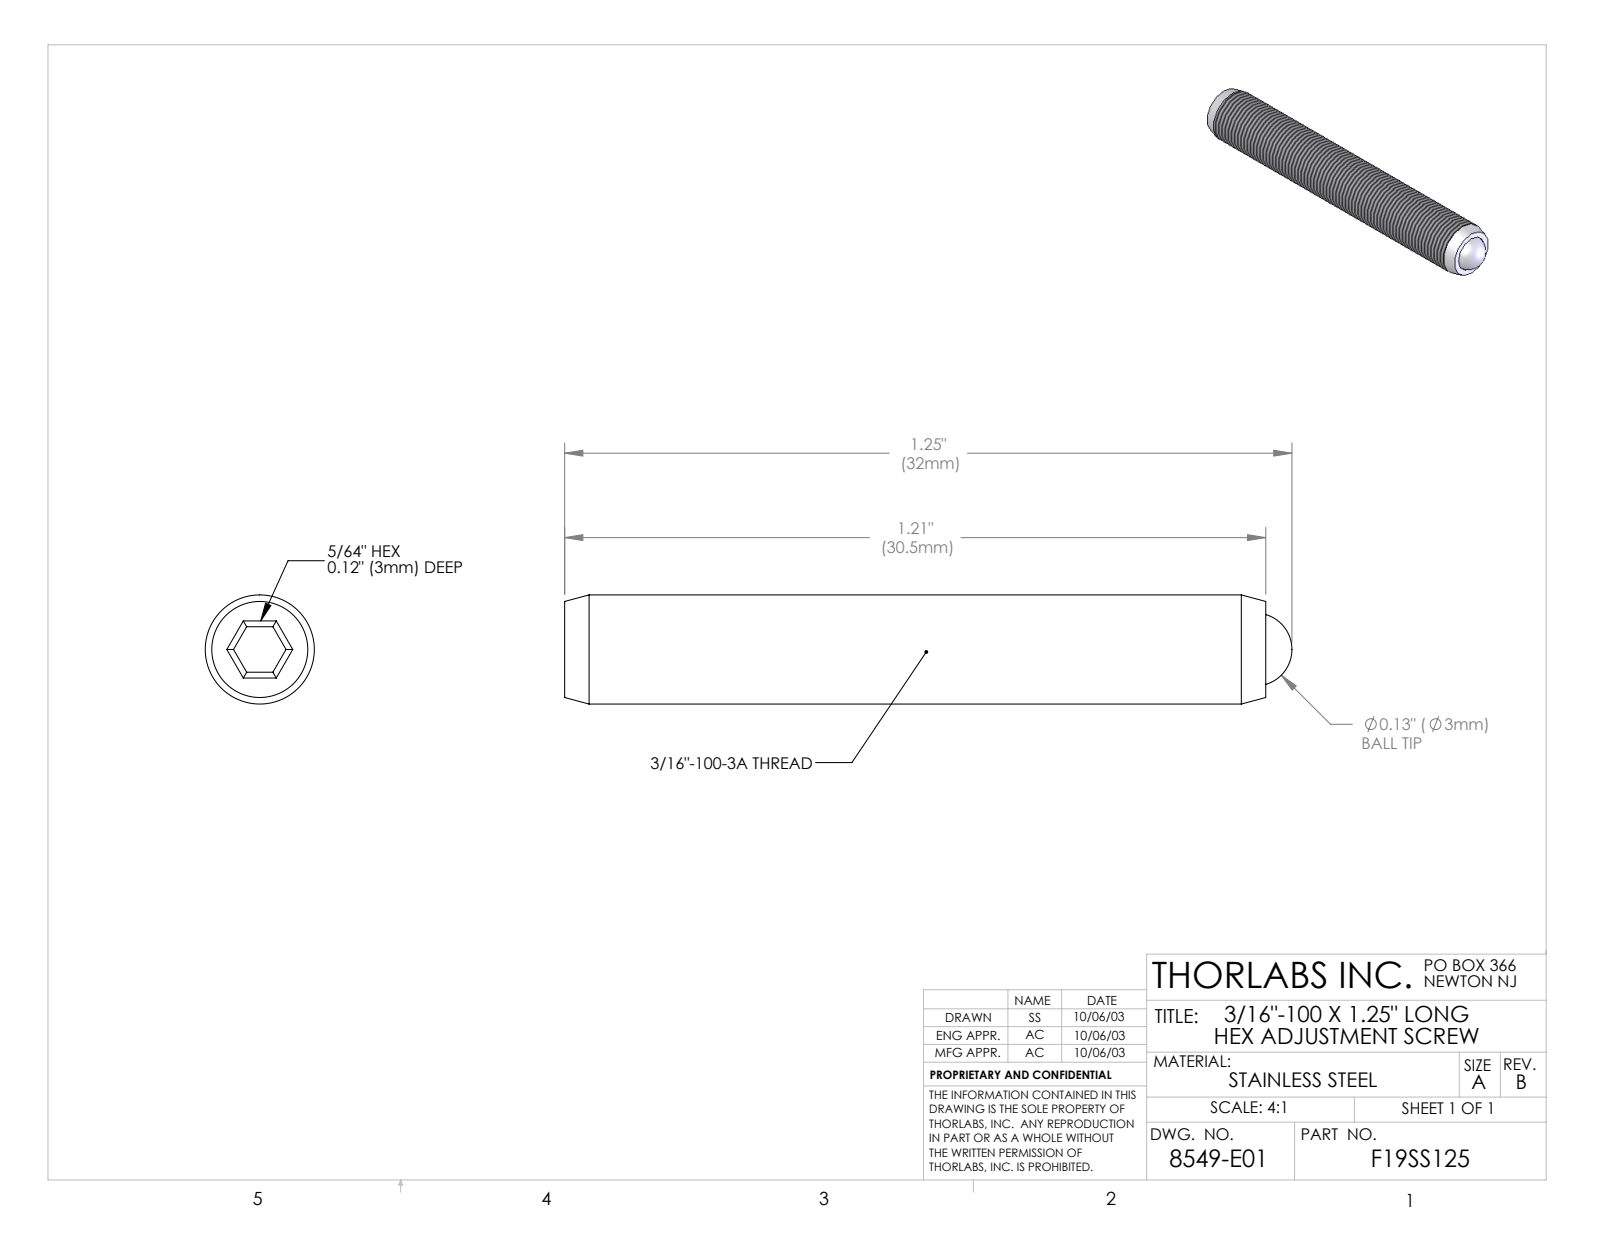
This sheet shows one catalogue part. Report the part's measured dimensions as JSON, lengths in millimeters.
{"part_name": "8549-E0W", "step_written_by": "SolidWorks 2007 (AUTOMOTIVE_DESIGN)", "units": "millimeters", "bodies": {"solids": 2, "faces": 29, "planar": 15, "cylindrical": 4, "other": 10}, "overall_size": [31.75, 4.76, 4.76], "volume_mm3": 534, "surface_area_mm2": 551, "round_holes": [[3.19, 1]], "round_bosses_or_shafts": [[4.76, 1]], "face_to_face_distances": [1.98, 30.61, 3.05, 27.56, 1.99]}
